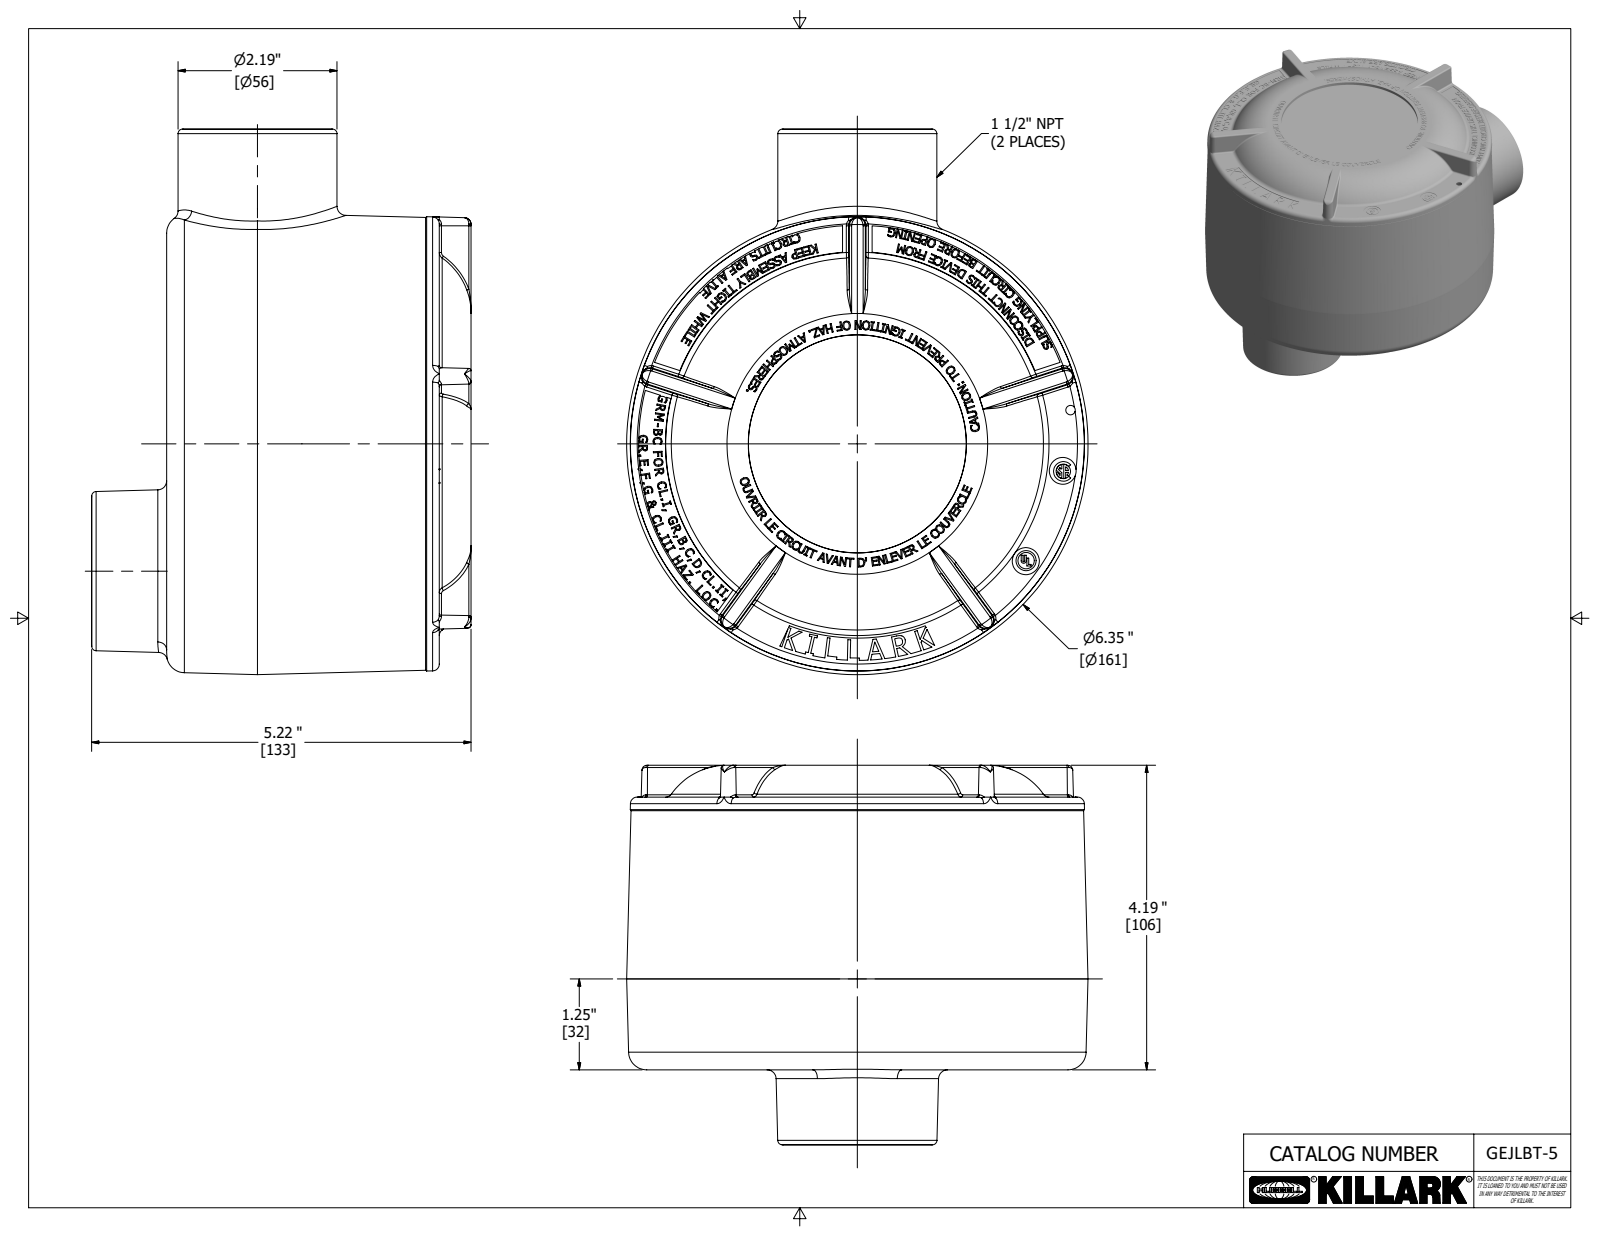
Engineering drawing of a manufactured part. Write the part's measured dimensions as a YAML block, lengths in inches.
part_name: "GEJLBT-5; 0071680M; 17805ABAM"
step_written_by: "Autodesk Inventor 2020 (AUTOMOTIVE_DESIGN)"
units: inches
bodies: {solids: 2, faces: 5367, planar: 2729, cylindrical: 235, other: 2403}
overall_size: [7.501, 6.346, 5.219]
volume: 47.61
surface_area: 322
round_holes:
  - {diameter: 1.558, count: 2}
  - {diameter: 0.13, count: 1}
  - {diameter: 0.196, count: 1}
  - {diameter: 0.225, count: 1}
  - {diameter: 0.369, count: 1}
  - {diameter: 0.372, count: 1}
  - {diameter: 5.285, count: 1}
  - {diameter: 5.433, count: 1}
  - {diameter: 5.687, count: 1}
  - {diameter: 5.768, count: 1}
round_bosses_or_shafts:
  - {diameter: 5.373, count: 1}
  - {diameter: 2.187, count: 1}
  - {diameter: 0.276, count: 1}
partial_cylinders:
  - {radius: 0.031, count: 20}
  - {radius: 0.062, count: 11}
  - {radius: 0.009, count: 1}
  - {radius: 0.034, count: 1}
  - {radius: 0.071, count: 1}
  - {radius: 0.098, count: 1}
  - {radius: 0.1, count: 1}
  - {radius: 0.135, count: 1}
face_to_face_distances: [3.563, 0.219, 3.781, 4.125, 0.563, 0.344, 0.031, 3.75, 0.062, 4.187]
hole_center_spacings: [0.842, 1.333, 1.342, 1.75, 1.752, 2.159, 2.167, 2.25]
